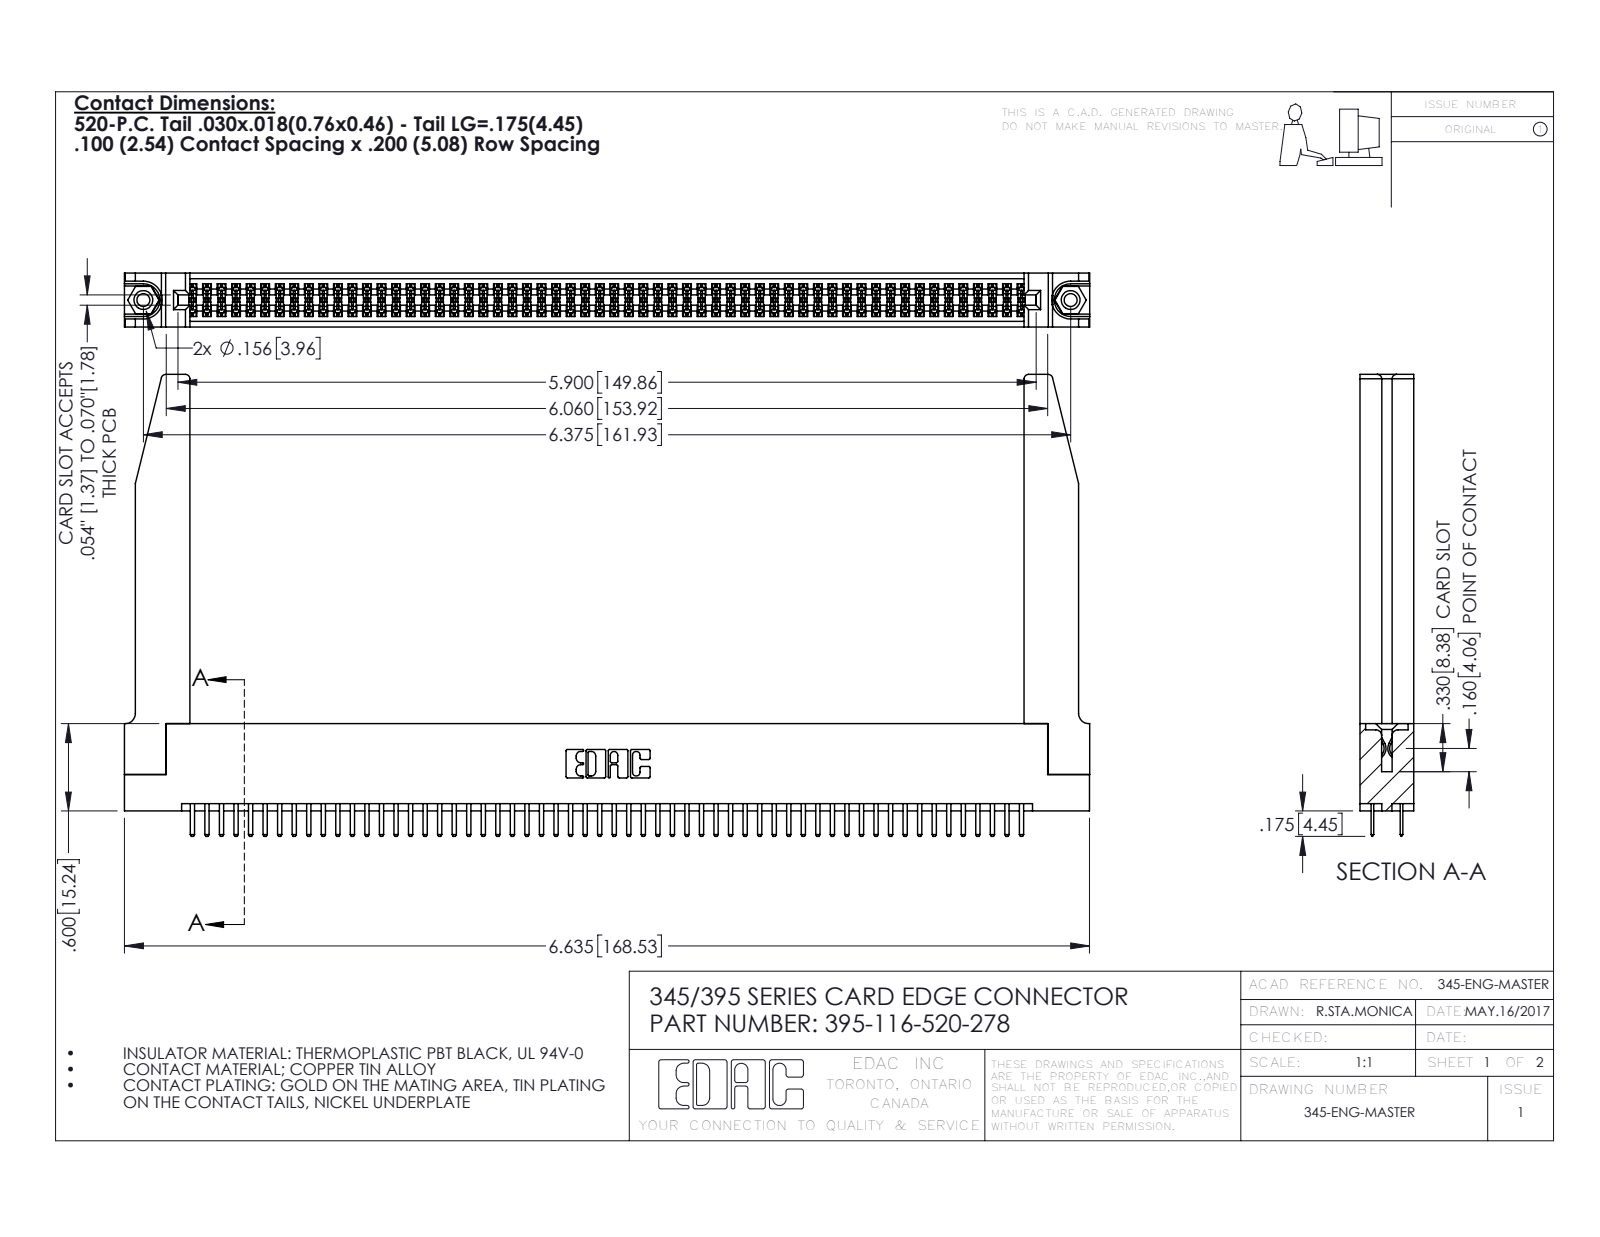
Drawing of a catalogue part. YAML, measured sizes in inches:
part_name: "395-116-520-278; 345 Part_Flush Mounting Lugs - 0.156 Dia-TH; 345-220-078_345-220-078; 345-250-001_345-250-001-102 (+1 more)"
step_written_by: "SolidWorks 2016 (CONFIG_CONTROL_DESIGN)"
units: inches
bodies: {solids: 121, faces: 6624, planar: 4282, cylindrical: 2290, other: 52}
overall_size: [6.636, 3.175, 0.37]
volume: 1.479
surface_area: 48.65
round_holes:
  - {diameter: 0.089, count: 2}
  - {diameter: 0.125, count: 2}
  - {diameter: 0.156, count: 2}
  - {diameter: 0.064, count: 1}
round_bosses_or_shafts:
  - {diameter: 0.155, count: 2}
partial_cylinders:
  - {radius: 0.006, count: 174}
  - {radius: 0.01, count: 120}
  - {radius: 0.01, count: 22}
  - {radius: 0.03, count: 8}
  - {radius: 0.007, count: 6}
  - {radius: 0.031, count: 6}
  - {radius: 0.026, count: 3}
  - {radius: 0.014, count: 2}
face_to_face_distances: [0.072, 0.37, 0.298, 0.2, 0.098, 0.272, 0.025, 0.225, 0.022, 0.072]
hole_center_spacings: [0.27, 6.139, 6.375]
